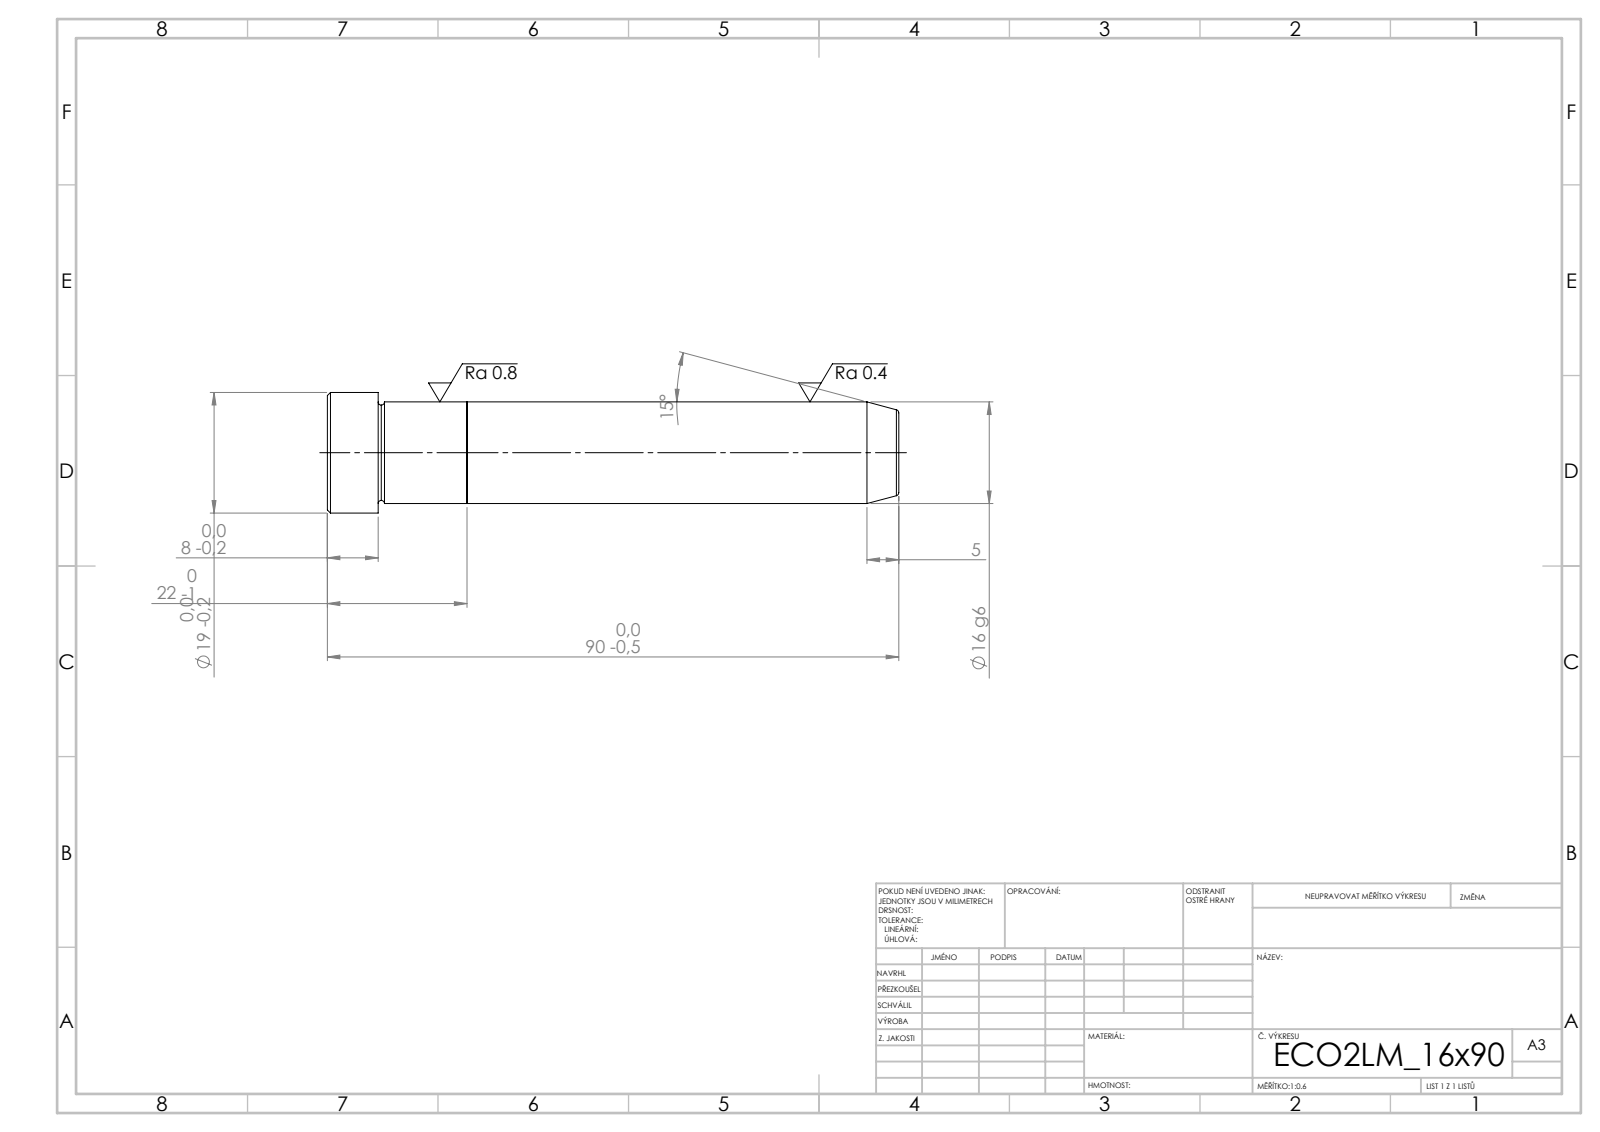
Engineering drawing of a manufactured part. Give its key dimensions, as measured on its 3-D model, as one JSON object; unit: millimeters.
{"step_written_by": "SolidWorks 2019 (CONFIG_CONTROL_DESIGN)", "units": "millimeters", "bodies": {"solids": 2, "faces": 21, "planar": 5, "cylindrical": 6, "other": 10}, "overall_size": [90, 19, 19], "volume_mm3": 18569, "surface_area_mm2": 5497, "round_bosses_or_shafts": [[19, 1], [16, 1]], "face_to_face_distances": [22, 68, 90, 82, 14, 8]}
